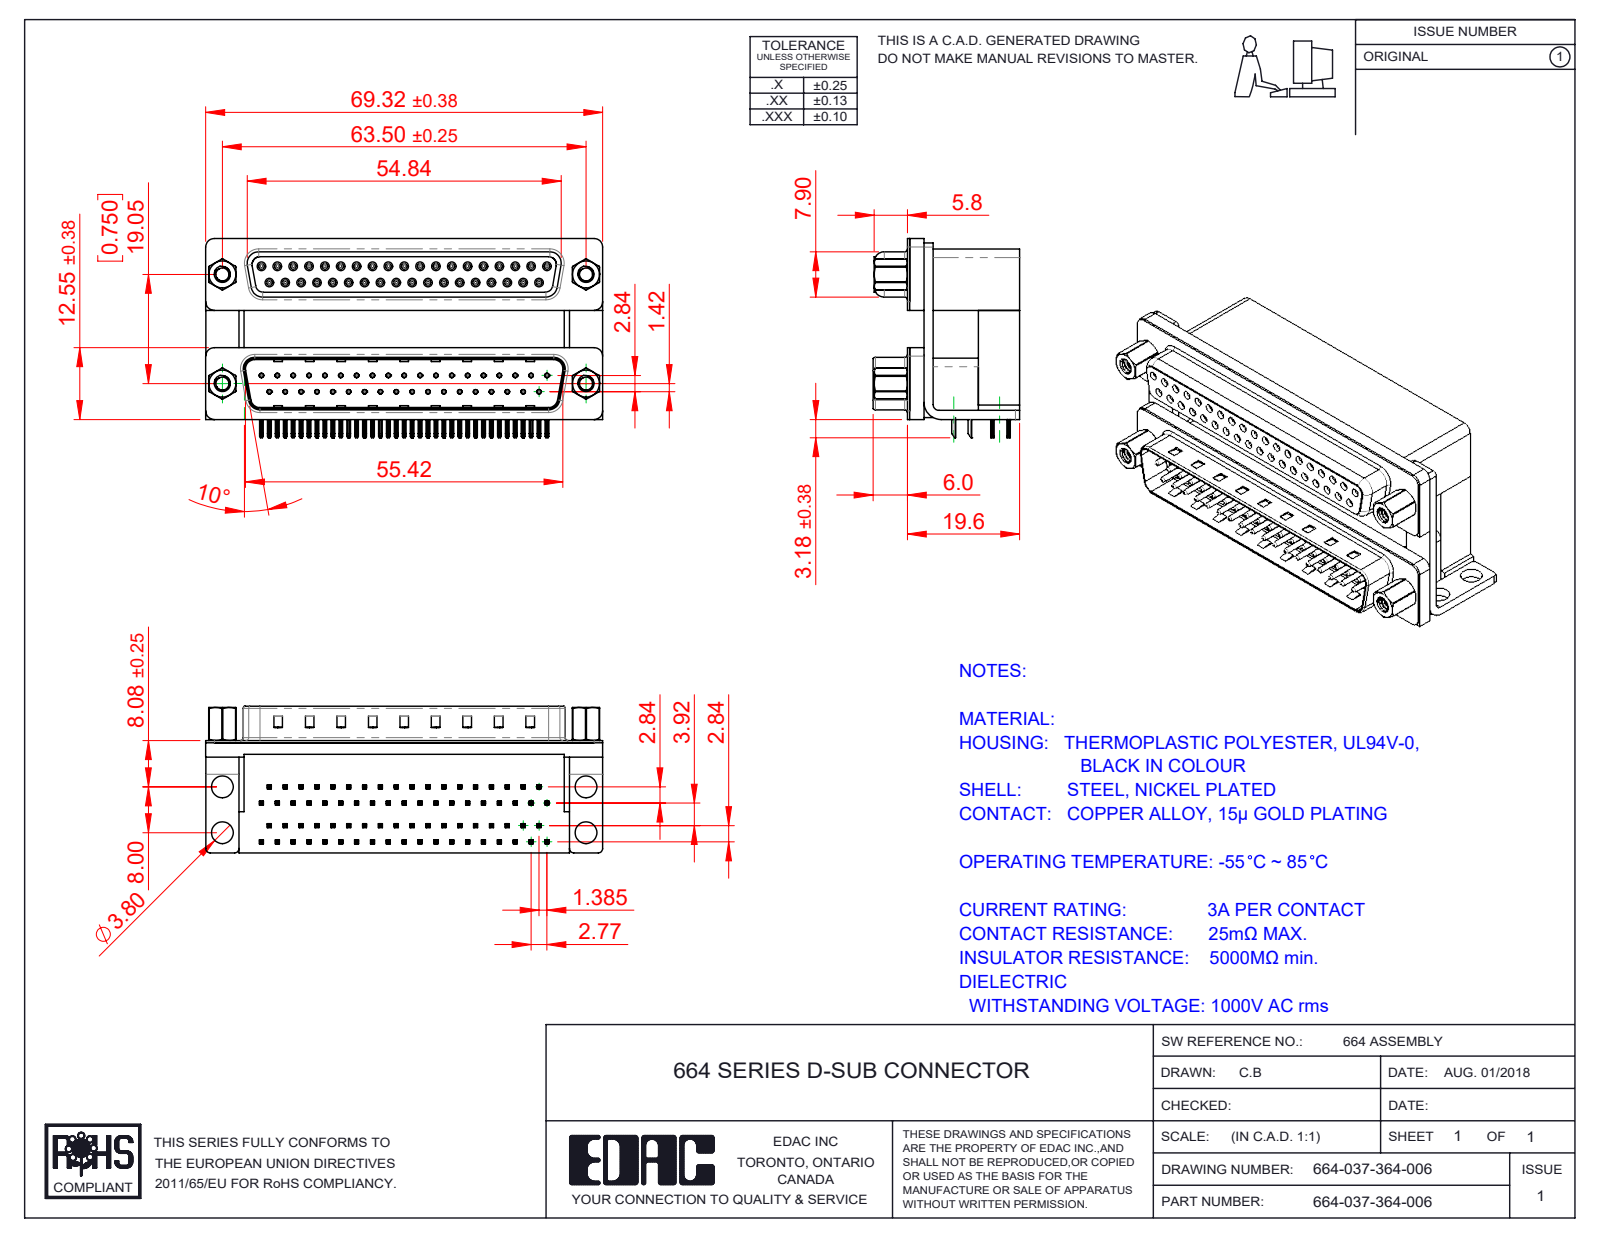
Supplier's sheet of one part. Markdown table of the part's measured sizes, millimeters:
| quantity | value |
| --- | --- |
| part name | 664 Shell Receptacle_37 Contacts; 664-037-364-006; 664 4-40 Hex Standoff 5; 664 Housing Upper_37 Contacts M (+8 more) |
| STEP written by | SolidWorks 2020 (CONFIG_CONTROL_DESIGN) |
| units | millimeters |
| bodies | 89 solids, 9197 faces (4785 planar, 2321 cylindrical, 2091 other) |
| overall size | 69.32 × 34.78 × 25.6 |
| volume | 31 513 mm³ |
| surface area | 33 567 mm² |
| round holes (diameter × count) | 0.8 × 74, 0.35 × 37, 0.9 × 37, 2.26 × 4, 2.29 × 4, 3.5 × 4, 3.8 × 4, 4 × 4, 4.8 × 4, 5 × 4 |
| round bosses / shafts (diameter × count) | 1.2 × 37, 0.75 × 37, 4.9 × 4, 4.75 × 4, 3.9 × 4, 2.79 × 4 |
| partial cylindrical surfaces (radius × count) | 0.1 × 296, 0.15 × 148, 0.25 × 148, 0.12 × 74, 0.35 × 74, 0.34 × 37, 0.28 × 18, 1.5 × 13 |
| main face-to-face distances | 0.4, 19.2, 7.2, 12, 10.69, 2.19, 2.84, 18.7, 29.39, 19.05 |
| hole center spacings | 2.77, 5.54, 3.16, 8.31, 11.08, 13.85, 16.62, 19.39 |
